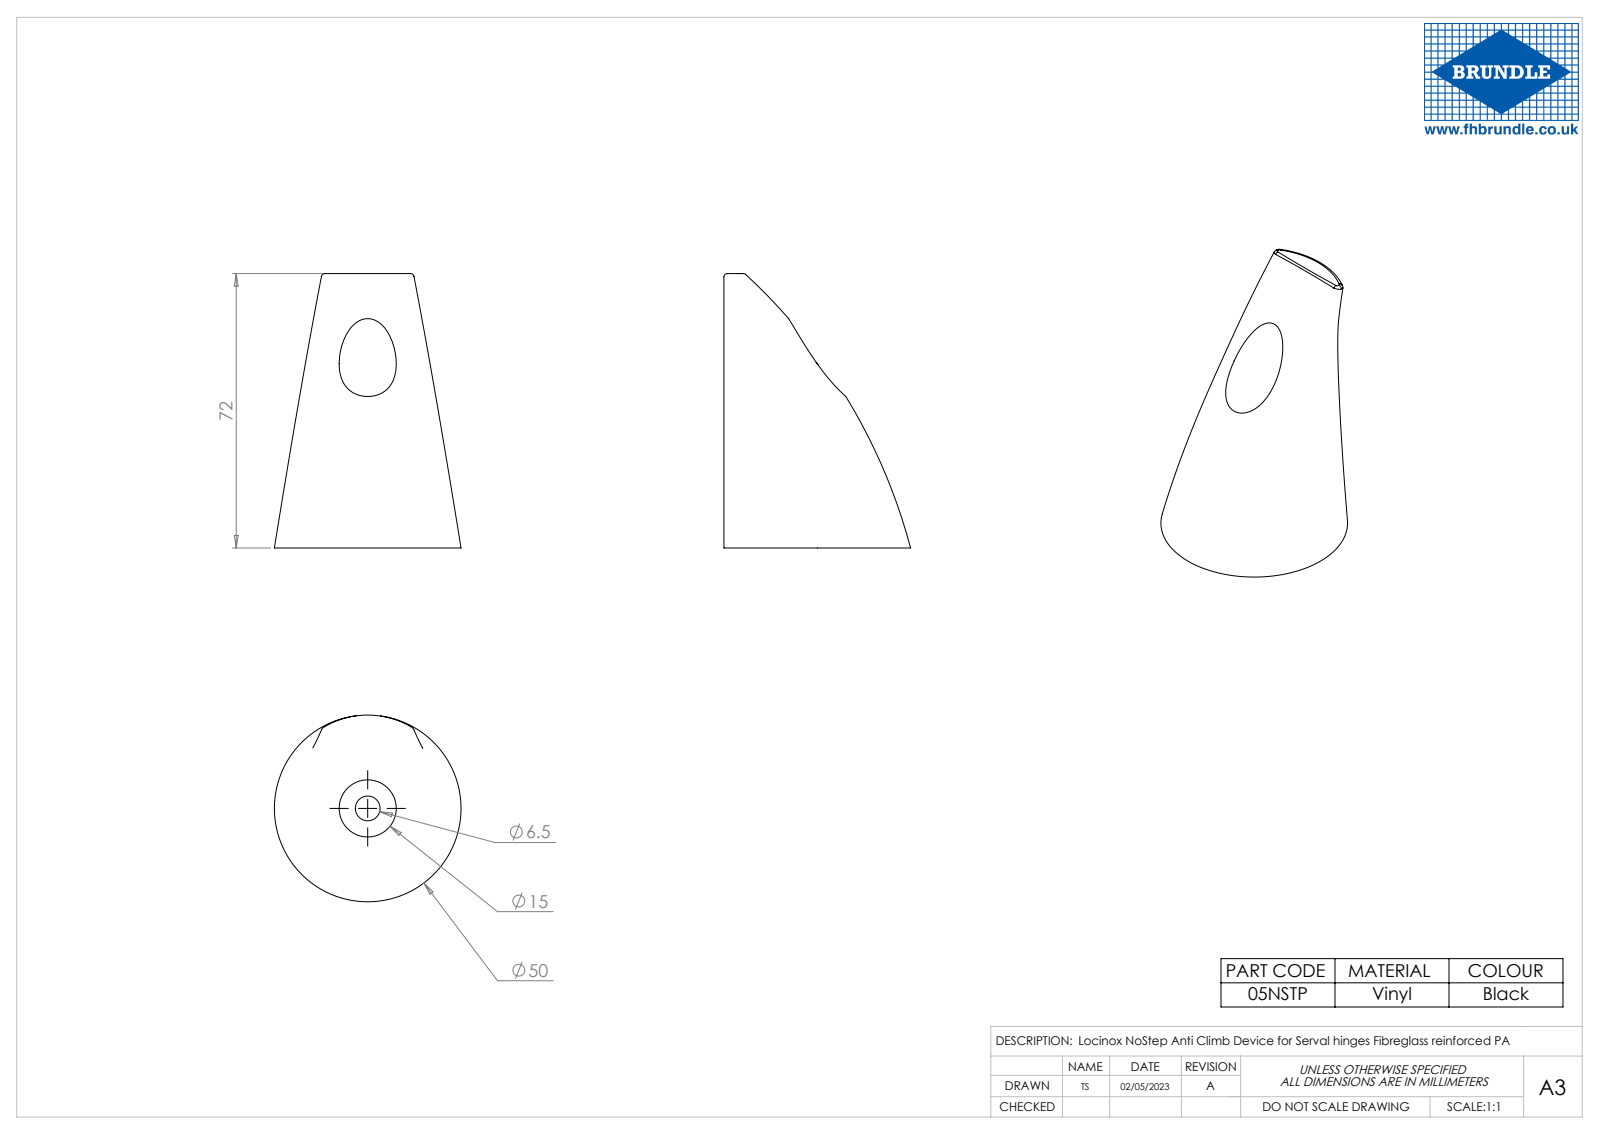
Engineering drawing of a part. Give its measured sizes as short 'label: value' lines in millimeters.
name: 05NSTP
written by: SolidWorks 2023 (CONFIG_CONTROL_DESIGN)
unit: mm
bodies: 1 solid, 17 faces (3 planar, 4 cylindrical, 10 other)
size: 72 × 49 × 49
volume: 62 932 mm³; area: 11 789 mm²
holes: 1× ⌀6.5, 1× ⌀15
face distances: 16, 72, 56
